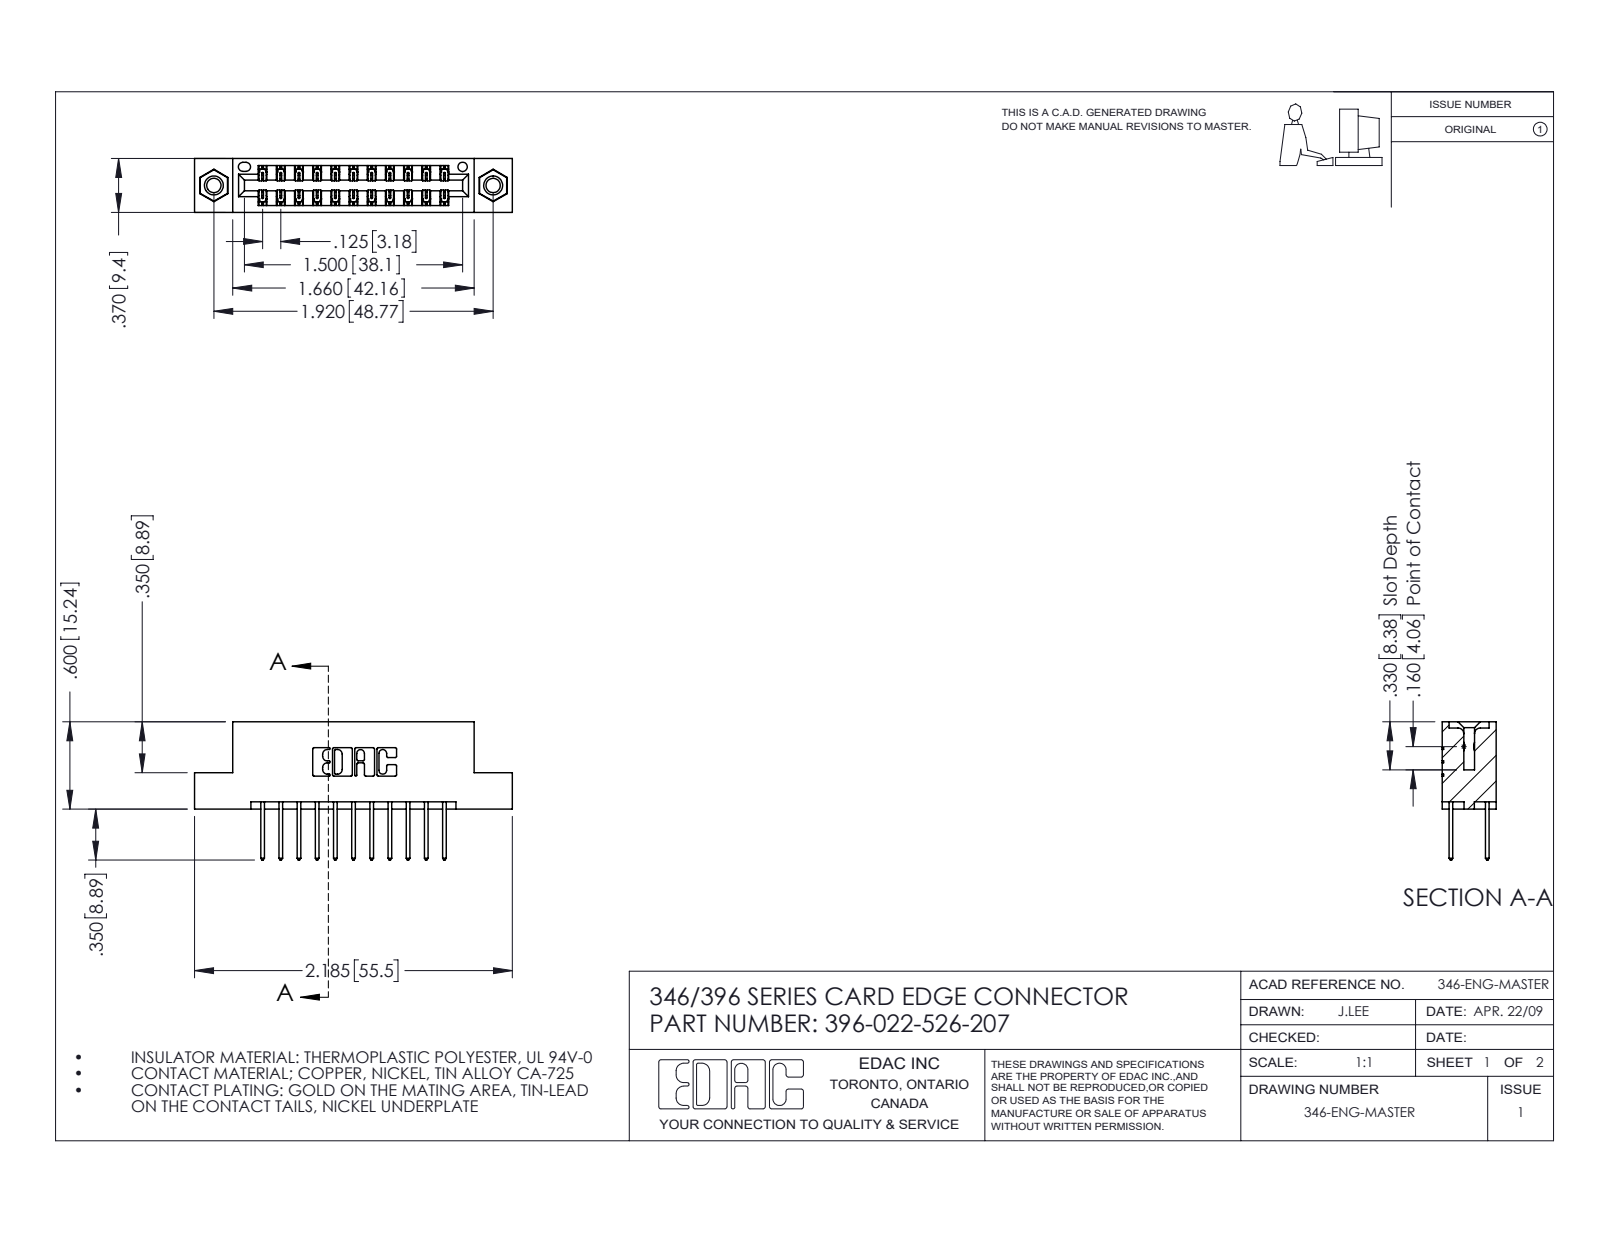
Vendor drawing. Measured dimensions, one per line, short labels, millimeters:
name: 396-022-526-207; 345-250-001_345-250-005-103; 346 Part_Flush Mounting Lugs - 0.156 Dia-TI; 345-292-001_345-293-126
written by: SolidWorks 2016 (CONFIG_CONTROL_DESIGN)
unit: mm
bodies: 25 solids, 1326 faces (878 planar, 432 cylindrical, 16 other)
size: 55.5 × 24.1 × 9.4
volume: 5 190 mm³; area: 6 845 mm²
holes: 2× ⌀2.5, 2× ⌀3.2, 2× ⌀4, 1× ⌀1.6
bosses: 2× ⌀3.9
rounds: 33× R0.2, 22× R0.3, 22× R0.3, 6× R0.2, 6× R0.8, 3× R0.7, 2× R0.4, 2× R0.6
face distances: 6.4, 1.2, 8.2, 9.4, 1.8, 7.6, 0.6, 7, 3.8, 5.6
hole spacings: 6.2, 43.6, 48.8
